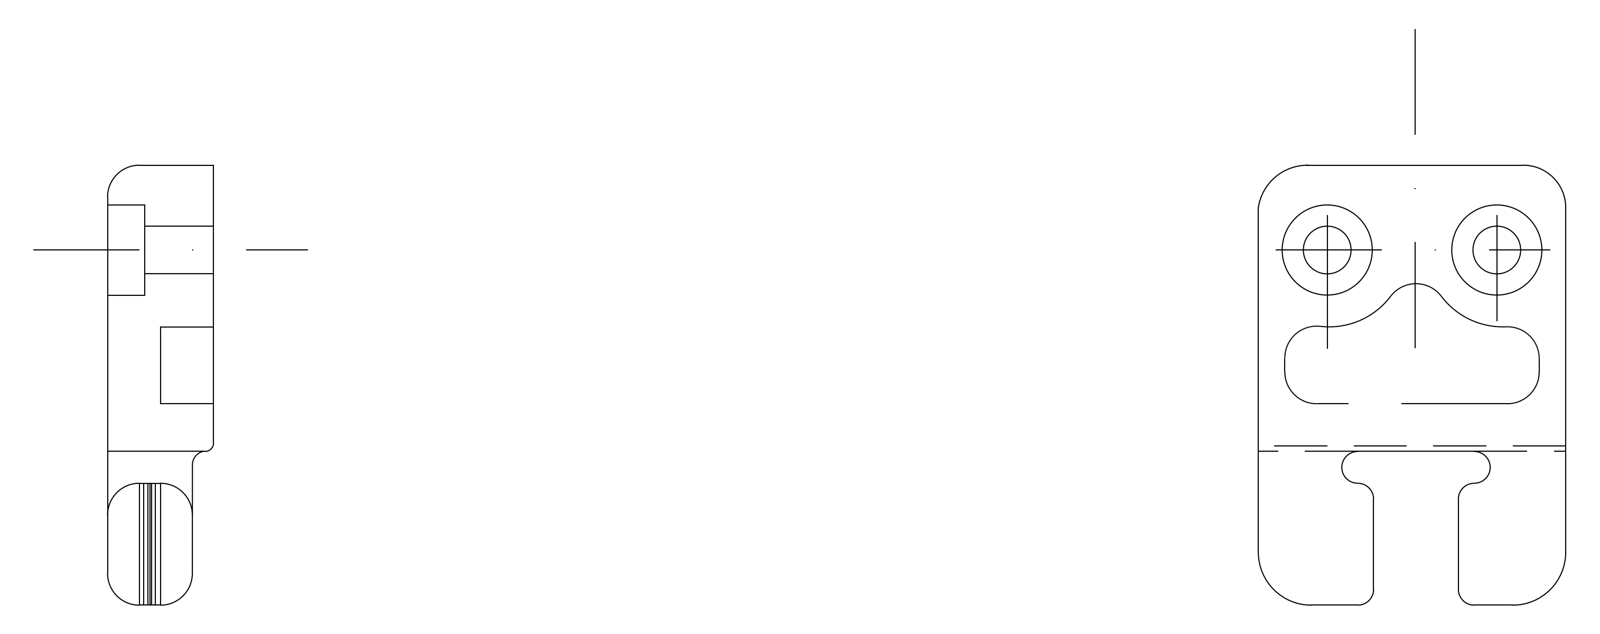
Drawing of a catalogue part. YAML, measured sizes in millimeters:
step_written_by: "THINKDESIGN (CONFIG_CONTROL_DESIGN)"
units: millimeters
bodies: {solids: 1, faces: 67, planar: 16, cylindrical: 31, other: 20}
overall_size: [41.52, 29, 10]
volume: 8963
surface_area: 3841
round_holes:
  - {diameter: 4.5, count: 2}
  - {diameter: 8.5, count: 2}
partial_cylinders:
  - {radius: 1, count: 7}
  - {radius: 2, count: 6}
  - {radius: 0.5, count: 5}
  - {radius: 1.5, count: 2}
  - {radius: 5, count: 2}
  - {radius: 4.53, count: 1}
  - {radius: 5.03, count: 1}
face_to_face_distances: [10, 8, 2, 29, 5, 10.5, 18.5, 3, 26.5, 1]
hole_center_spacings: [16]
